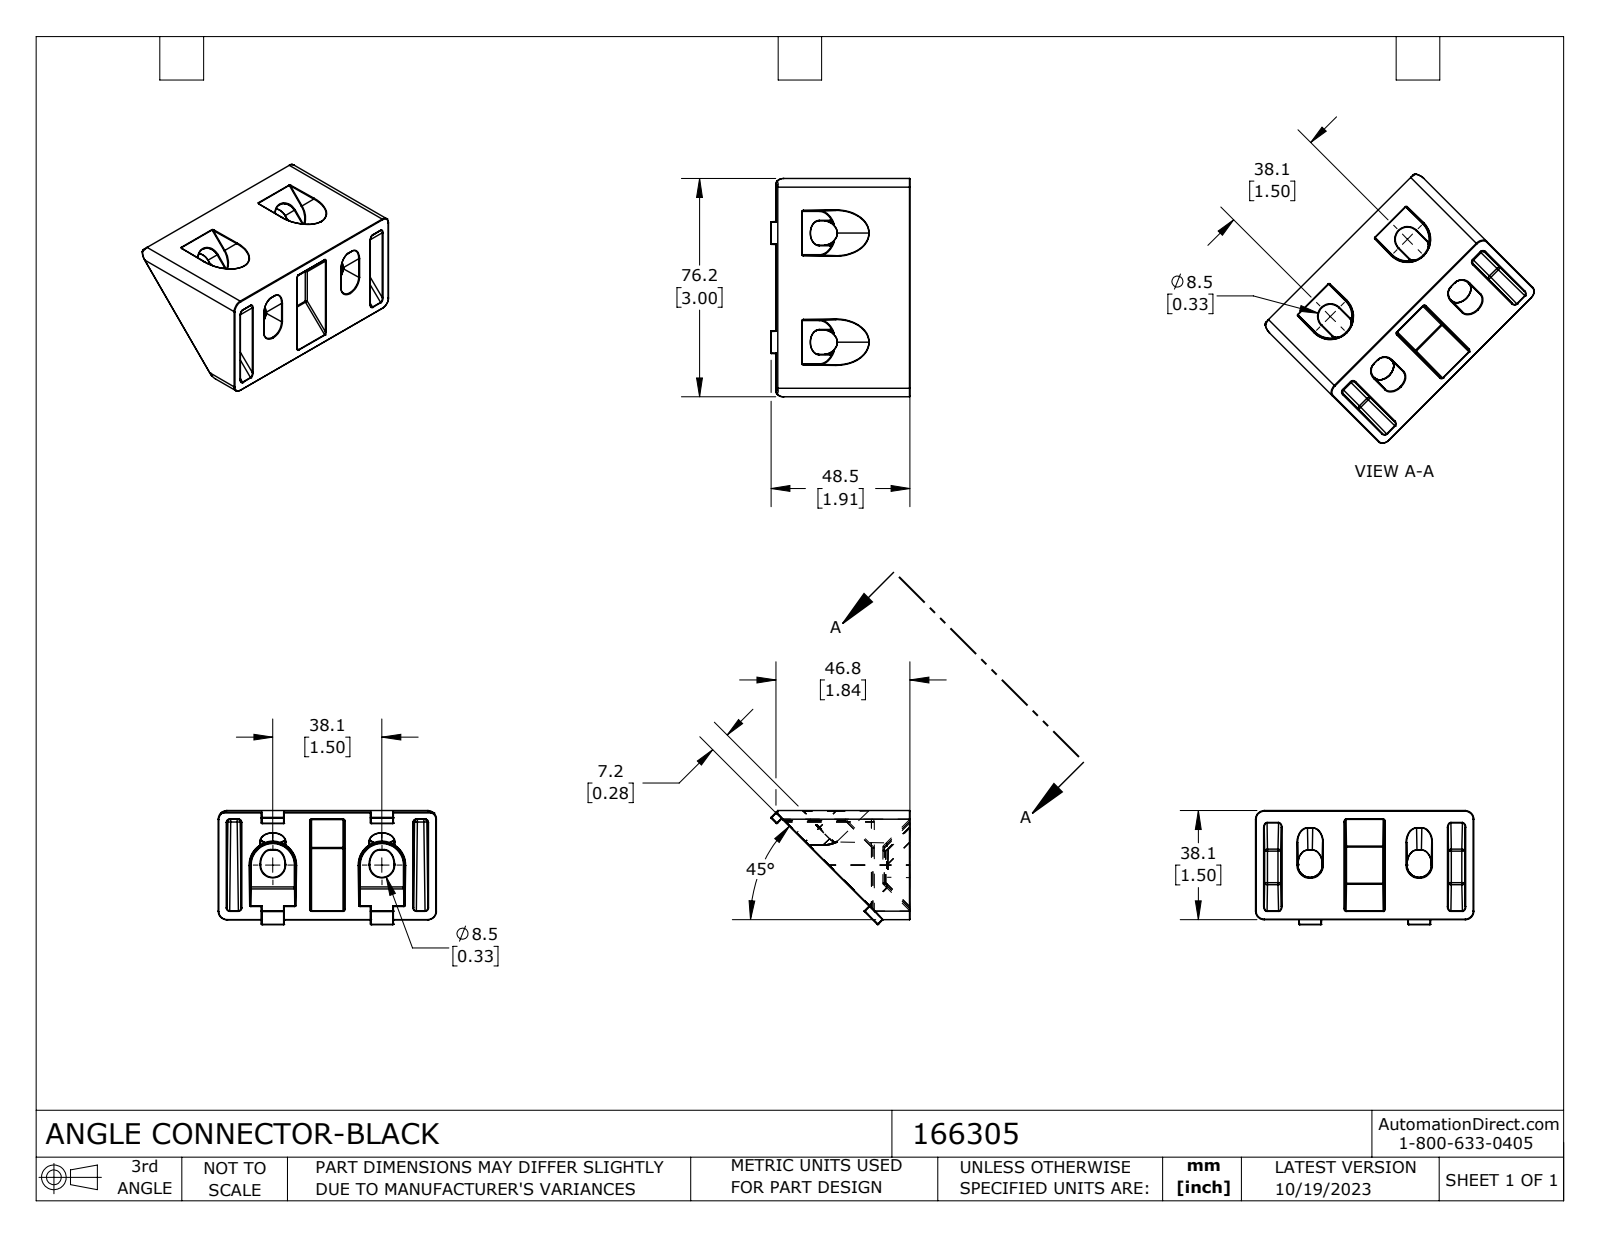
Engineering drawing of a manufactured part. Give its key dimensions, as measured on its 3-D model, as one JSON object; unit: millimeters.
{"part_name": "166305", "step_written_by": "SolidWorks 2023 (CONFIG_CONTROL_DESIGN)", "units": "millimeters", "bodies": {"solids": 1, "faces": 425, "planar": 75, "cylindrical": 170, "other": 180}, "overall_size": [76.2, 48.58, 39.78], "volume_mm3": 51174, "surface_area_mm2": 20361, "partial_cylinders_radius": [[0.2, 89], [1, 24], [0.5, 16], [3, 4], [3.5, 4]], "face_to_face_distances": [38.1, 76.2, 65.2, 32.1, 44.1, 3, 12, 12.5, 35.1, 4.44]}
